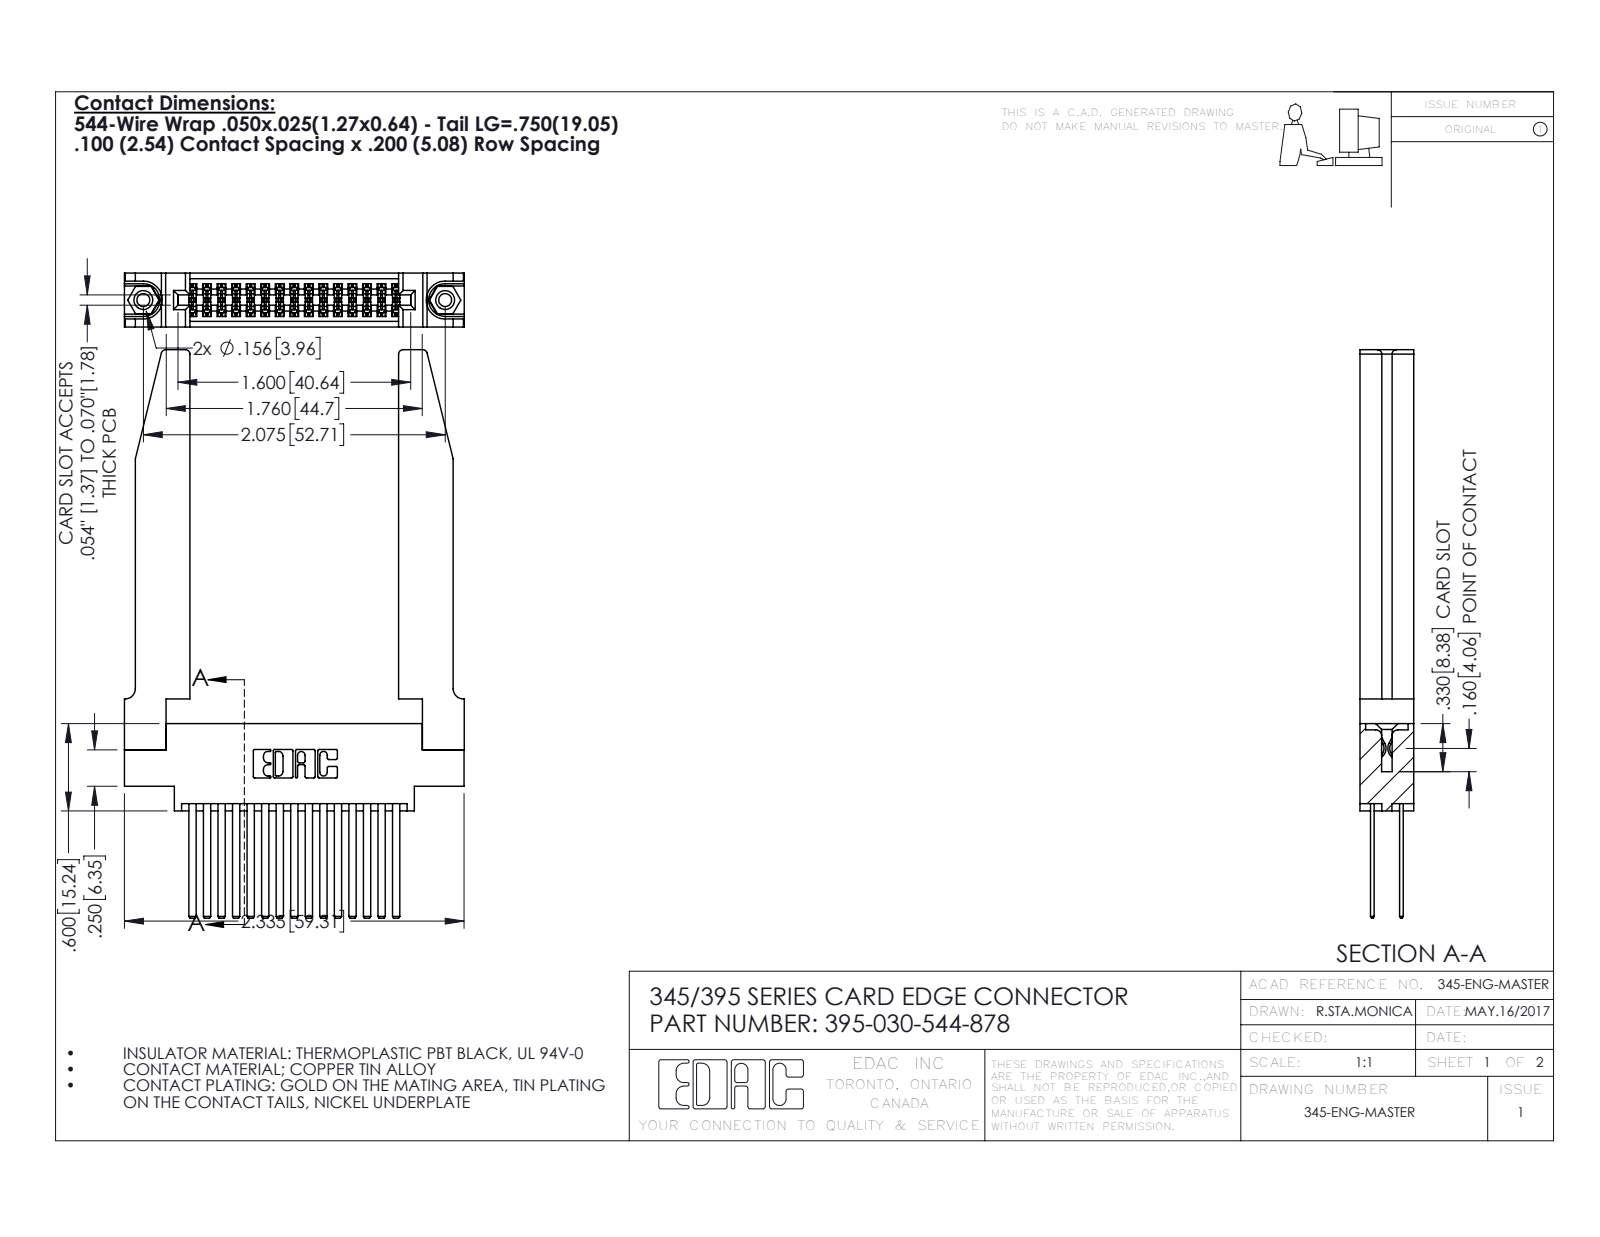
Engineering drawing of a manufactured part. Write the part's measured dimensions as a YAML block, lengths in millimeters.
part_name: "345-220-078_345-220-078; 395-030-544-878; 345-250-001_345-250-001-102; 345-292-001_345-293-144 (+1 more)"
step_written_by: "SolidWorks 2016 (CONFIG_CONTROL_DESIGN)"
units: millimeters
bodies: {solids: 35, faces: 1684, planar: 1096, cylindrical: 536, other: 52}
overall_size: [99.2, 59.3, 9.4]
volume: 13600
surface_area: 16300
round_holes:
  - {diameter: 2.3, count: 2}
  - {diameter: 3.2, count: 2}
  - {diameter: 4, count: 2}
  - {diameter: 1.6, count: 1}
round_bosses_or_shafts:
  - {diameter: 3.9, count: 2}
partial_cylinders:
  - {radius: 0.2, count: 45}
  - {radius: 0.3, count: 22}
  - {radius: 0.8, count: 8}
  - {radius: 0.2, count: 6}
  - {radius: 0.8, count: 6}
  - {radius: 0.7, count: 3}
  - {radius: 0.4, count: 2}
  - {radius: 0.5, count: 2}
face_to_face_distances: [9.4, 1.8, 7.6, 2.5, 6.9, 0.6, 5.1, 5.7, 4.4, 3.8]
hole_center_spacings: [6.9, 46.8, 52.7]
